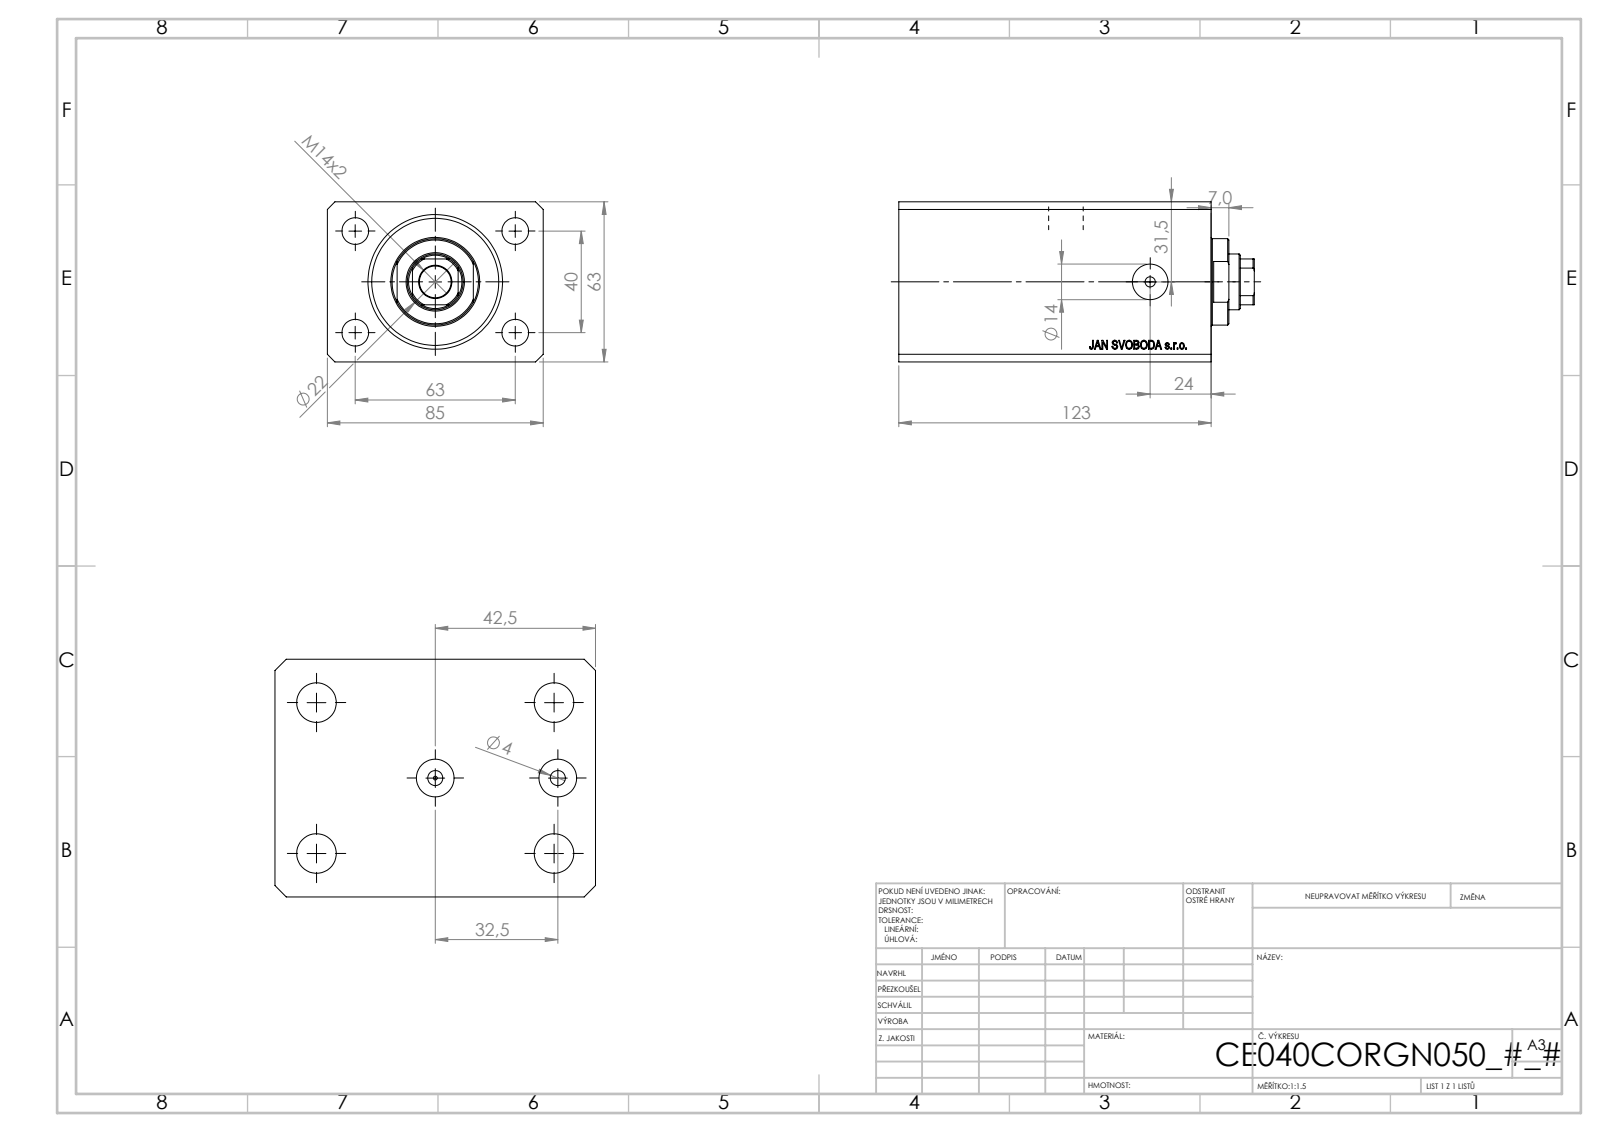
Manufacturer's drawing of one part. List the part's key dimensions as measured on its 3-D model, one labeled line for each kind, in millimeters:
Part name (STEP PRODUCT): V250CE_C_VCP; V250CE_VC_C; V250CE_C_Body
STEP written by: SolidWorks 2019 (CONFIG_CONTROL_DESIGN)
Units: millimetres
Bodies: 3 solids, 868 faces (428 planar, 46 cylindrical, 394 other)
Overall size (bounding box): 140 × 85 × 63
Volume: 572 992 mm³ · Surface area: 102 621 mm²
Round holes (diameter × count): ⌀4 ×4, ⌀10.5 ×4, ⌀10 ×2, ⌀14 ×2, ⌀1.25 ×1, ⌀12.5 ×1, ⌀22 ×1, ⌀40 ×1, ⌀53 ×1
Round bosses / shafts (diameter × count): ⌀34 ×1
Partial cylindrical surfaces — rounded edges, fillets, slot ends (radius × count): R10.5 ×1
Main face-to-face distances: 63, 85, 123, 17, 106, 11.4, 94.6, 111.6, 100.4, 56
Hole centre spacings: 37.31, 20.02, 40, 63, 67.05, 74.63, 32.5, 75
